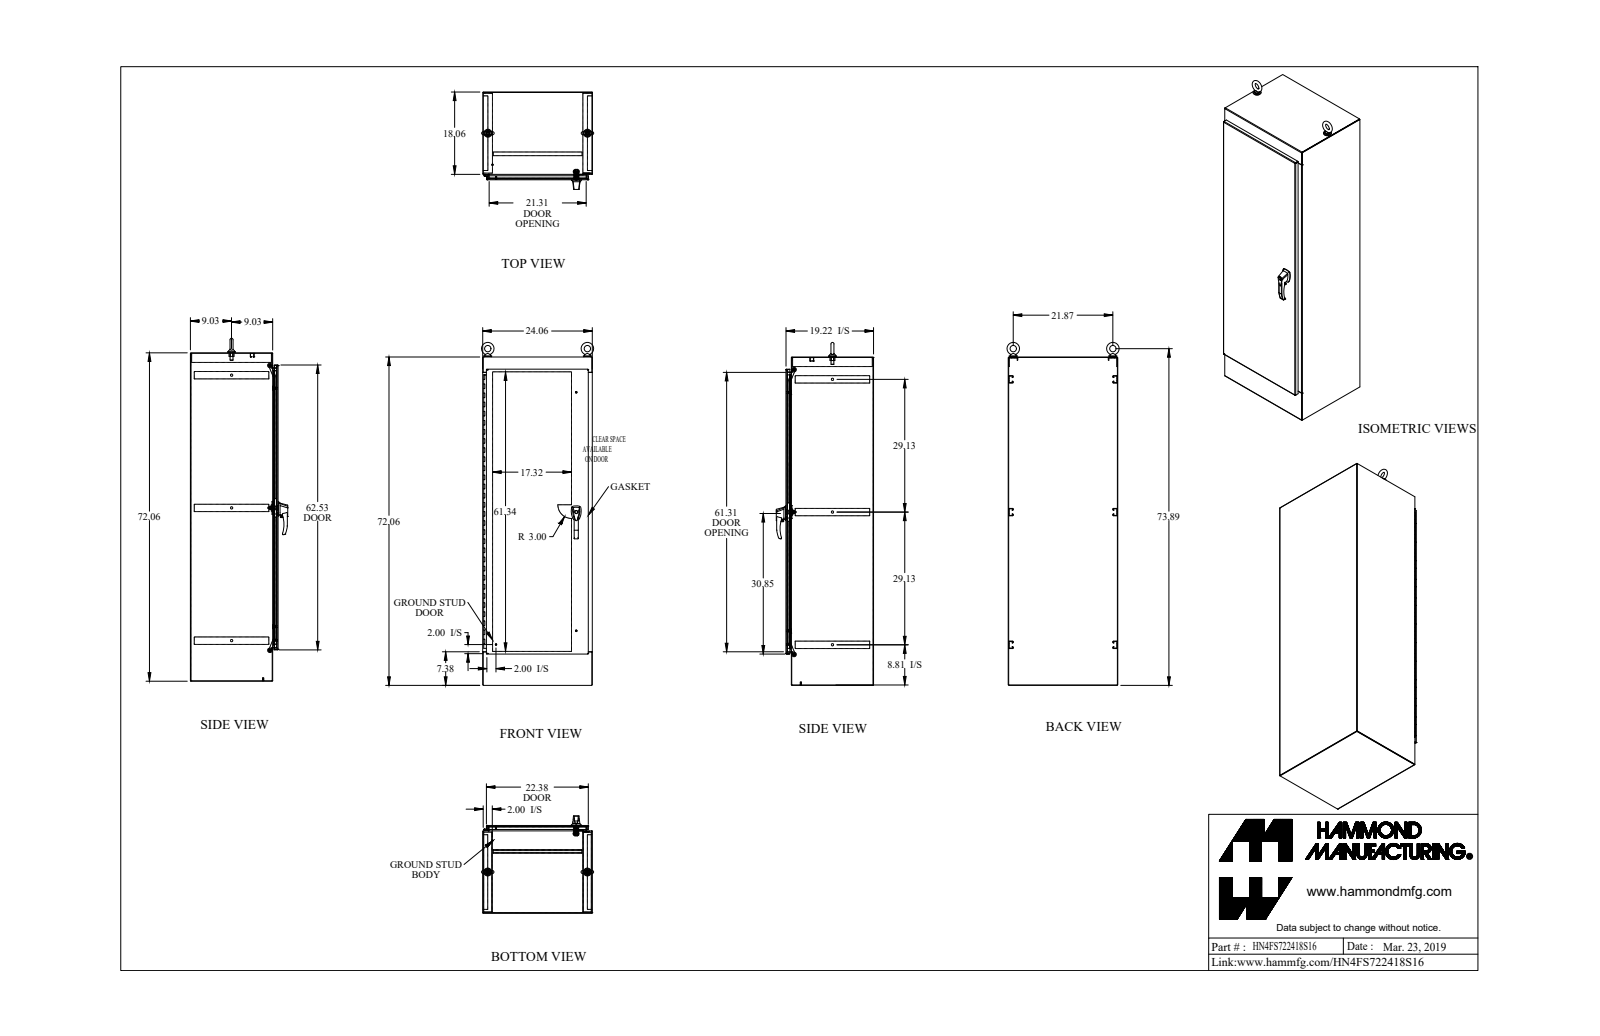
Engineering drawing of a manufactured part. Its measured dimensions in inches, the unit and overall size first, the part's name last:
Units: inches
Overall size (bounding box): 75.256 × 24.604 × 21.362
Round holes (diameter × count): ⌀0.304 ×10, ⌀0.35 ×7, ⌀0.5 ×3, ⌀0.25 ×2, ⌀0.257 ×2, ⌀0.28 ×2, ⌀0.281 ×2, ⌀0.313 ×2, ⌀0.39 ×2, ⌀0.413 ×2, ⌀0.527 ×2, ⌀0.625 ×2
Round bosses / shafts (diameter × count): ⌀1.75 ×2, ⌀1.5 ×2, ⌀1.25 ×2, ⌀1 ×2, ⌀0.75 ×2, ⌀0.738 ×2, ⌀0.63 ×2, ⌀0.44 ×2
Partial cylindrical surfaces — rounded edges, fillets, slot ends (radius × count): R0.043 ×42, R0.138 ×36, R0.5 ×23, R0.125 ×22, R0.017 ×16, R0.06 ×15, R0.048 ×13, R0.143 ×13
Main face-to-face distances: 0.095, 19.152, 23.965, 23.87, 19.057, 19.247, 24.06, 71.965, 17.965, 1.187
Hole centre spacings: 6, 12, 18, 24, 30, 36, 42, 0.015
Volume: 823.3 in³ · Surface area: 17 283 in²
Bodies: 56 solids, 1875 faces (862 planar, 848 cylindrical, 165 other)
Part name (STEP PRODUCT): HN4FS722418S16
STEP written by: SolidWorks 2018 (AUTOMOTIVE_DESIGN)
